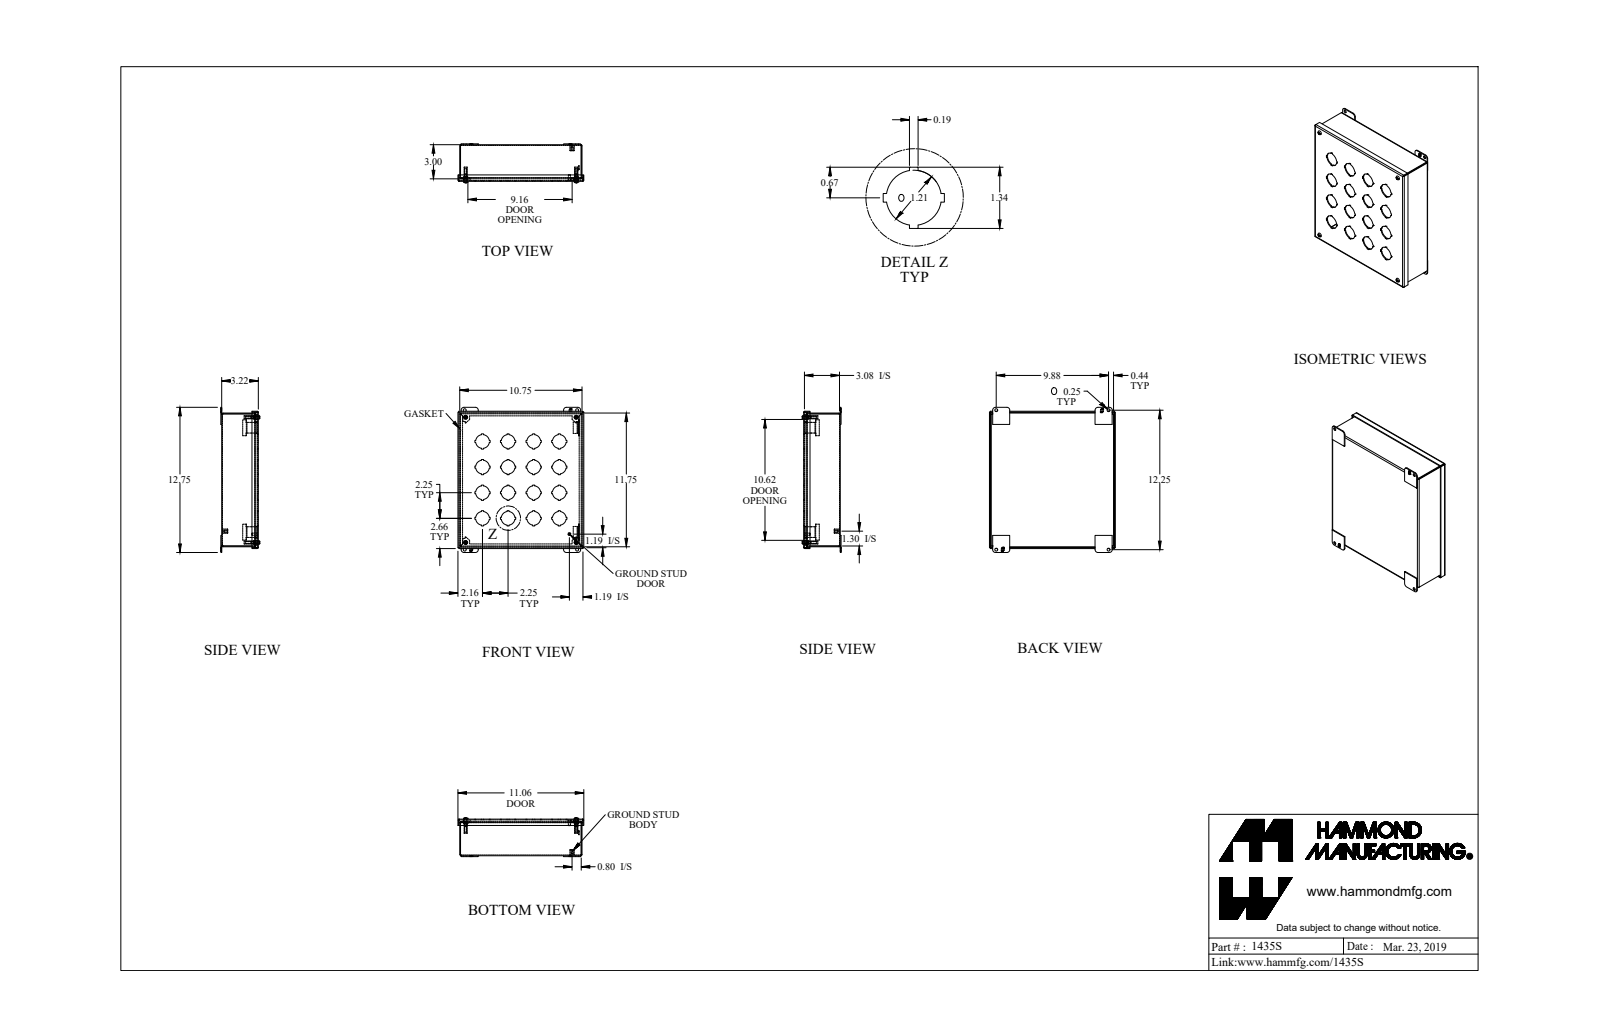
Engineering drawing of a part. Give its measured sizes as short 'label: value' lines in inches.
name: 1435S_Default
written by: SolidWorks 2019 (CONFIG_CONTROL_DESIGN)
unit: in
bodies: 23 solids, 971 faces (691 planar, 224 cylindrical, 56 other)
size: 12.75 × 11.062 × 3.421
volume: 34.03 in³; area: 905.2 in²
holes: 16× ⌀1.21, 8× ⌀0.25, 4× ⌀0.159, 4× ⌀0.406, 1× ⌀0.156
bosses: 4× ⌀0.39, 4× ⌀0.275, 4× ⌀0.19, 4× ⌀0.148, 1× ⌀0.375, 1× ⌀0.25, 1× ⌀0.188
rounds: 12× R0.036, 12× R0.108, 8× R0.25, 4× R0.029, 4× R0.086, 4× R0.16, 4× R0.171
face distances: 0.072, 3.15, 3.078, 3.222, 10.678, 0.072, 11.678, 10.606, 10.75, 0.156
hole spacings: 2.25, 5.031, 3.182, 4.5, 11, 7.115, 11.626, 6.364
